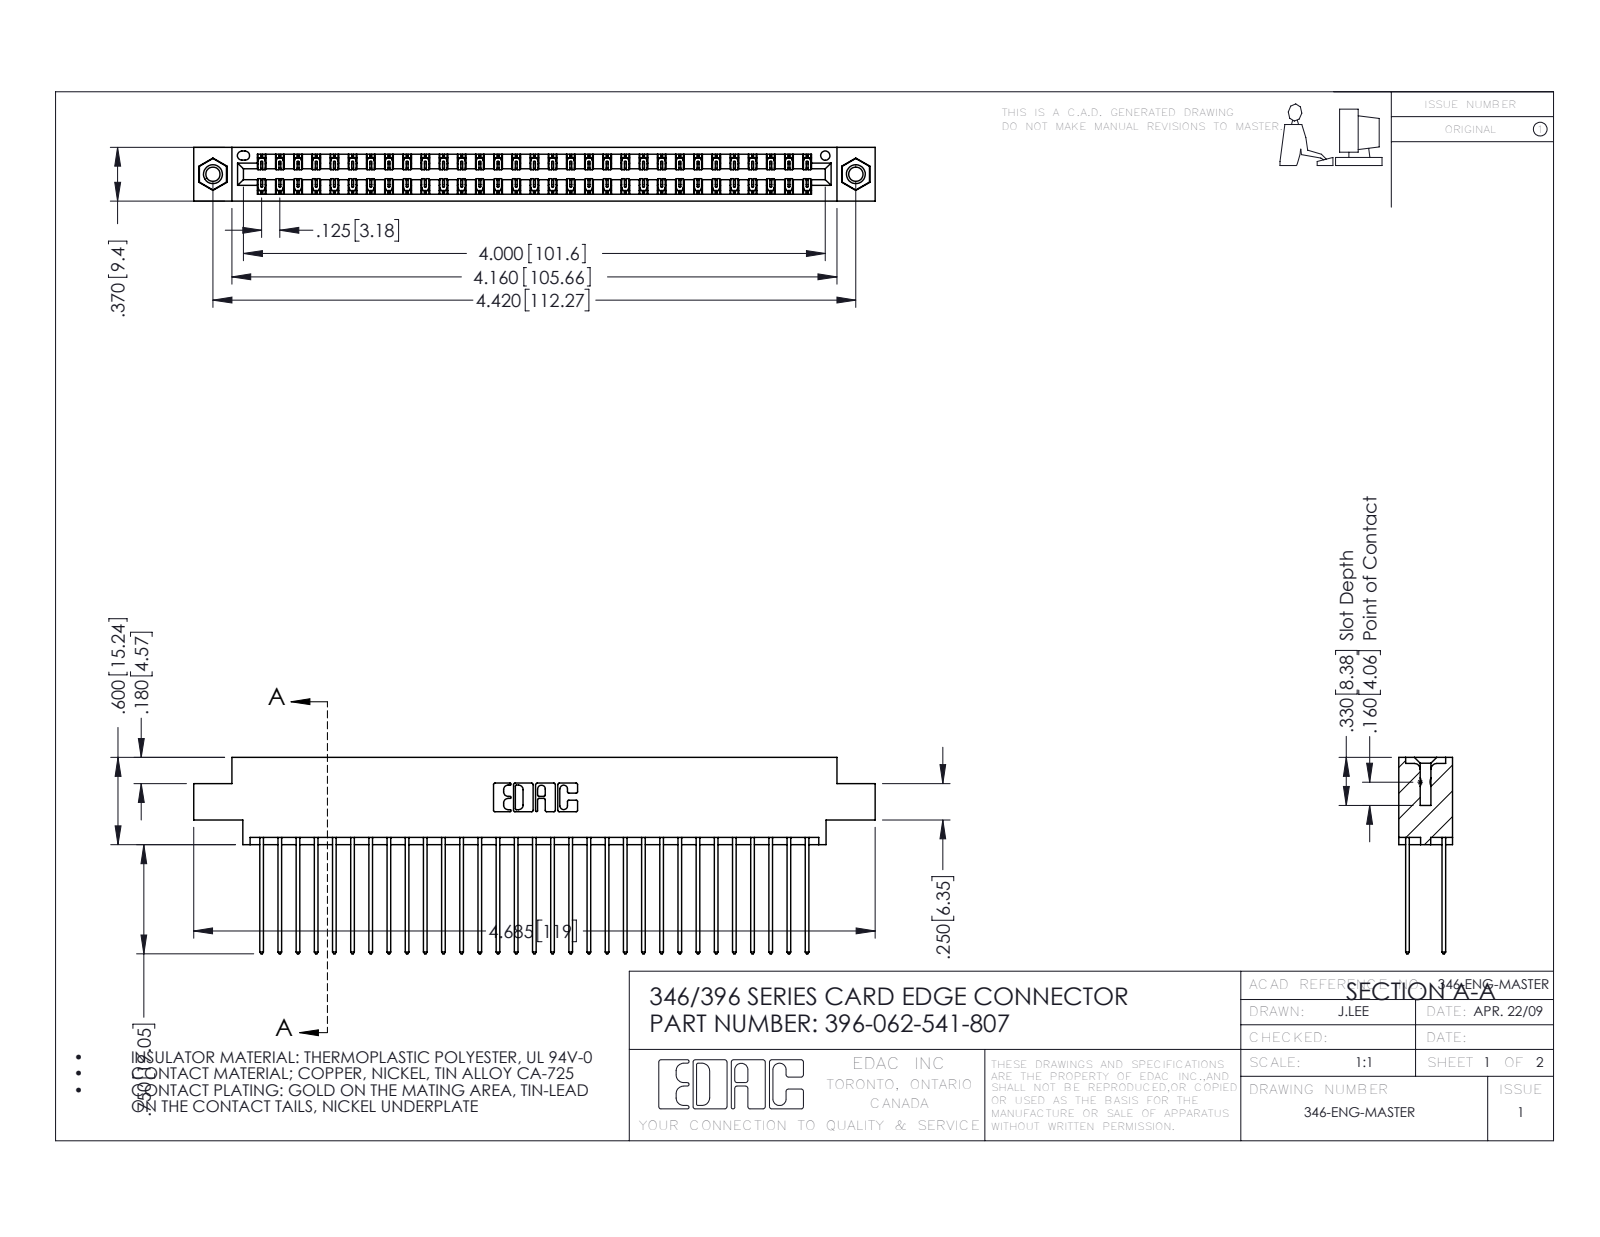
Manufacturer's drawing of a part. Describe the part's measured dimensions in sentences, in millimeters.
The part is named "345-292-001_345-293-141; 396-062-541-807; 345-250-001_345-250-005-103; 346 Part_0.170 Offset - 0.156 Dia-TI". Its 3-D file was written by "SolidWorks 2016 (CONFIG_CONTROL_DESIGN)". It is 65 solids with 3410 faces: 2282 planar, 1112 cylindrical and 16 other. Overall it measures 119 by 34.3 by 9.4 millimeters. Its volume is 11 700 cubic millimeters and its surface area 17 840 square millimeters. Round holes: 2 of diameter 2.5, 2 of diameter 3.2, 2 of diameter 4, 1 of diameter 1.6. Round bosses or shafts: 2 of diameter 3.9. Partial cylindrical surfaces (rounded edges, fillets, slot ends): 93 of radius 0.2, 62 of radius 0.3, 22 of radius 0.3, 6 of radius 0.2, 6 of radius 0.8, 3 of radius 0.7, 2 of radius 0.4, 2 of radius 0.6. The main face-to-face distances are 1.2, 8.2, 6.4, 1.8, 7.6, 0.6, 9.4, 7, 5.6, 3.8. The hole center spacings are 6.2, 107, 112.3.
